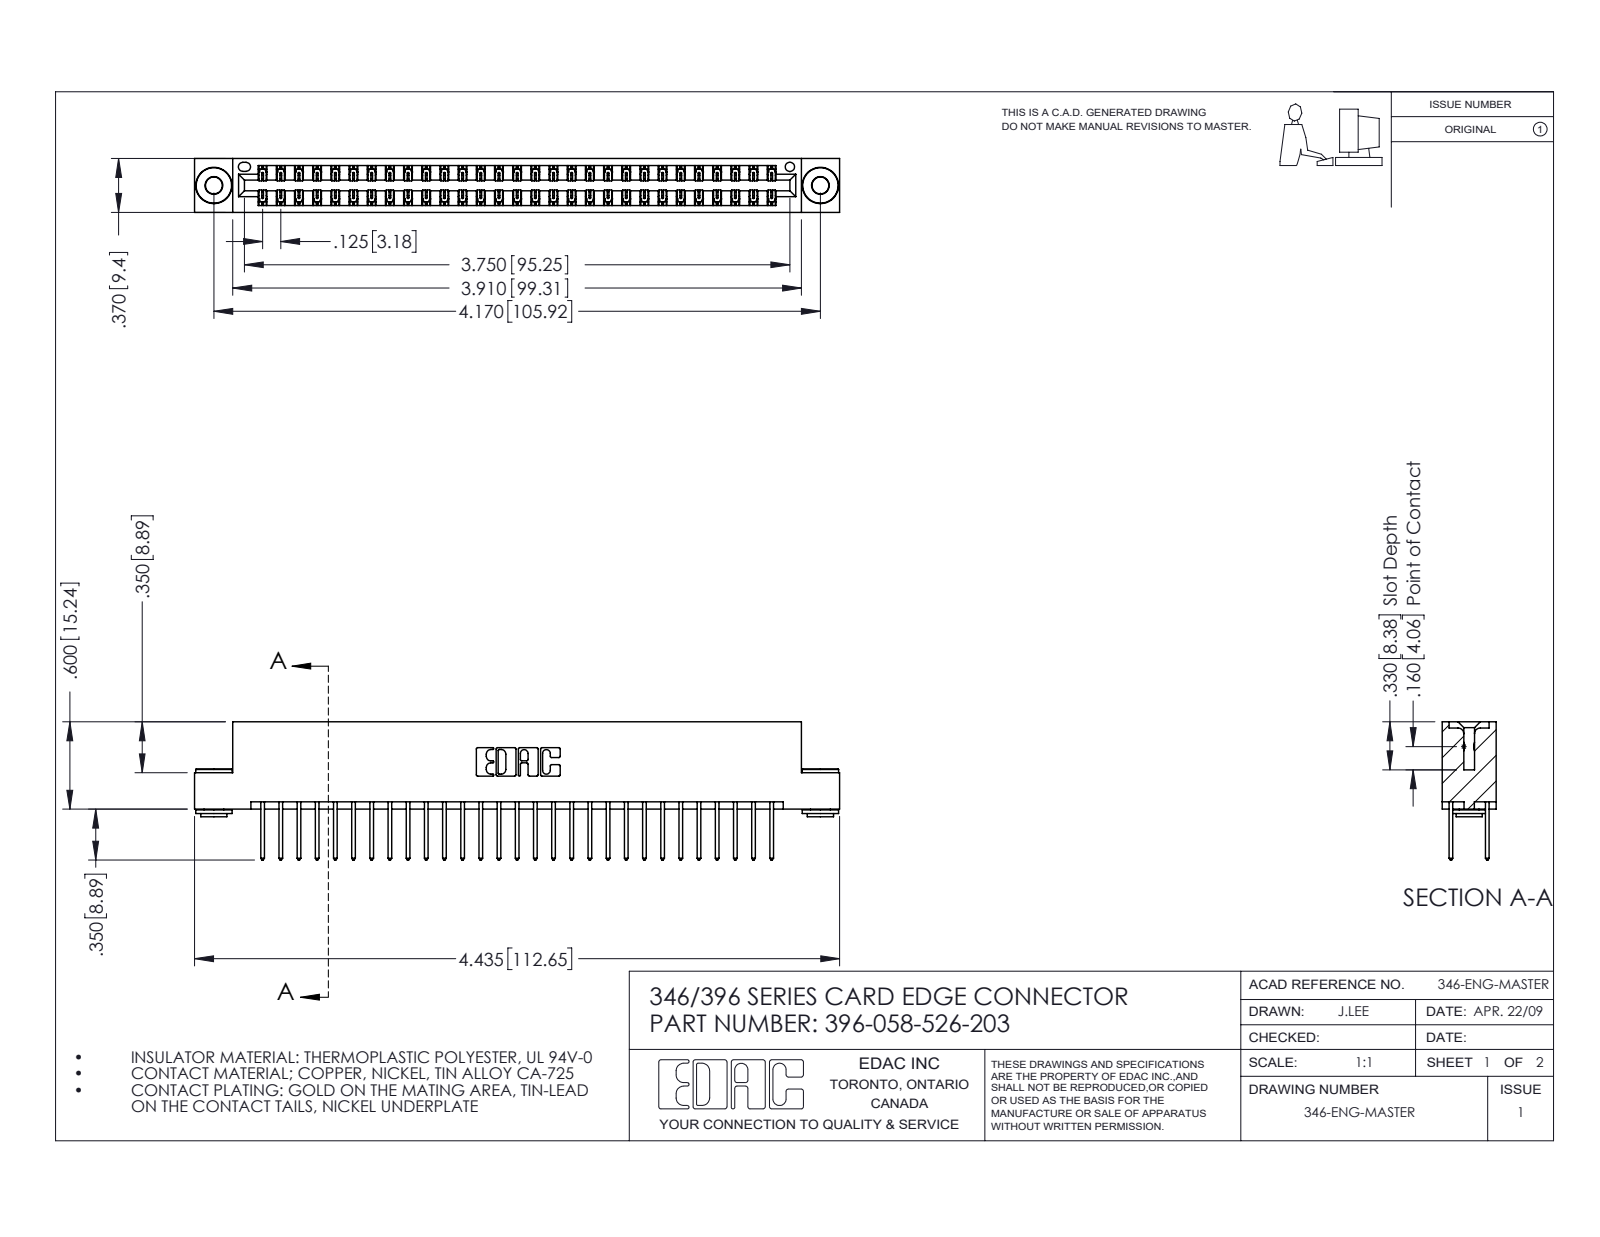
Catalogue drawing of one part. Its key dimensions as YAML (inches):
part_name: "396-058-526-203; 345-250-002_345-250-002-102; 346 Part_Flush Mounting Lugs - 0.156 Dia-TH; 345-292-001_345-293-126"
step_written_by: "SolidWorks 2016 (CONFIG_CONTROL_DESIGN)"
units: inches
bodies: {solids: 61, faces: 3176, planar: 2116, cylindrical: 1052, other: 8}
overall_size: [4.435, 0.95, 0.37]
volume: 0.671
surface_area: 24.11
round_holes:
  - {diameter: 0.116, count: 2}
  - {diameter: 0.156, count: 2}
  - {diameter: 0.064, count: 1}
round_bosses_or_shafts:
  - {diameter: 0.25, count: 2}
  - {diameter: 0.18, count: 2}
  - {diameter: 0.136, count: 2}
partial_cylinders:
  - {radius: 0.006, count: 87}
  - {radius: 0.01, count: 58}
  - {radius: 0.01, count: 22}
  - {radius: 0.007, count: 6}
  - {radius: 0.031, count: 6}
  - {radius: 0.026, count: 3}
  - {radius: 0.014, count: 2}
  - {radius: 0.022, count: 2}
face_to_face_distances: [0.048, 0.322, 0.25, 0.37, 0.025, 0.072, 0.298, 0.275, 0.148, 0.222]
hole_center_spacings: [0.246, 3.962, 4.17]
